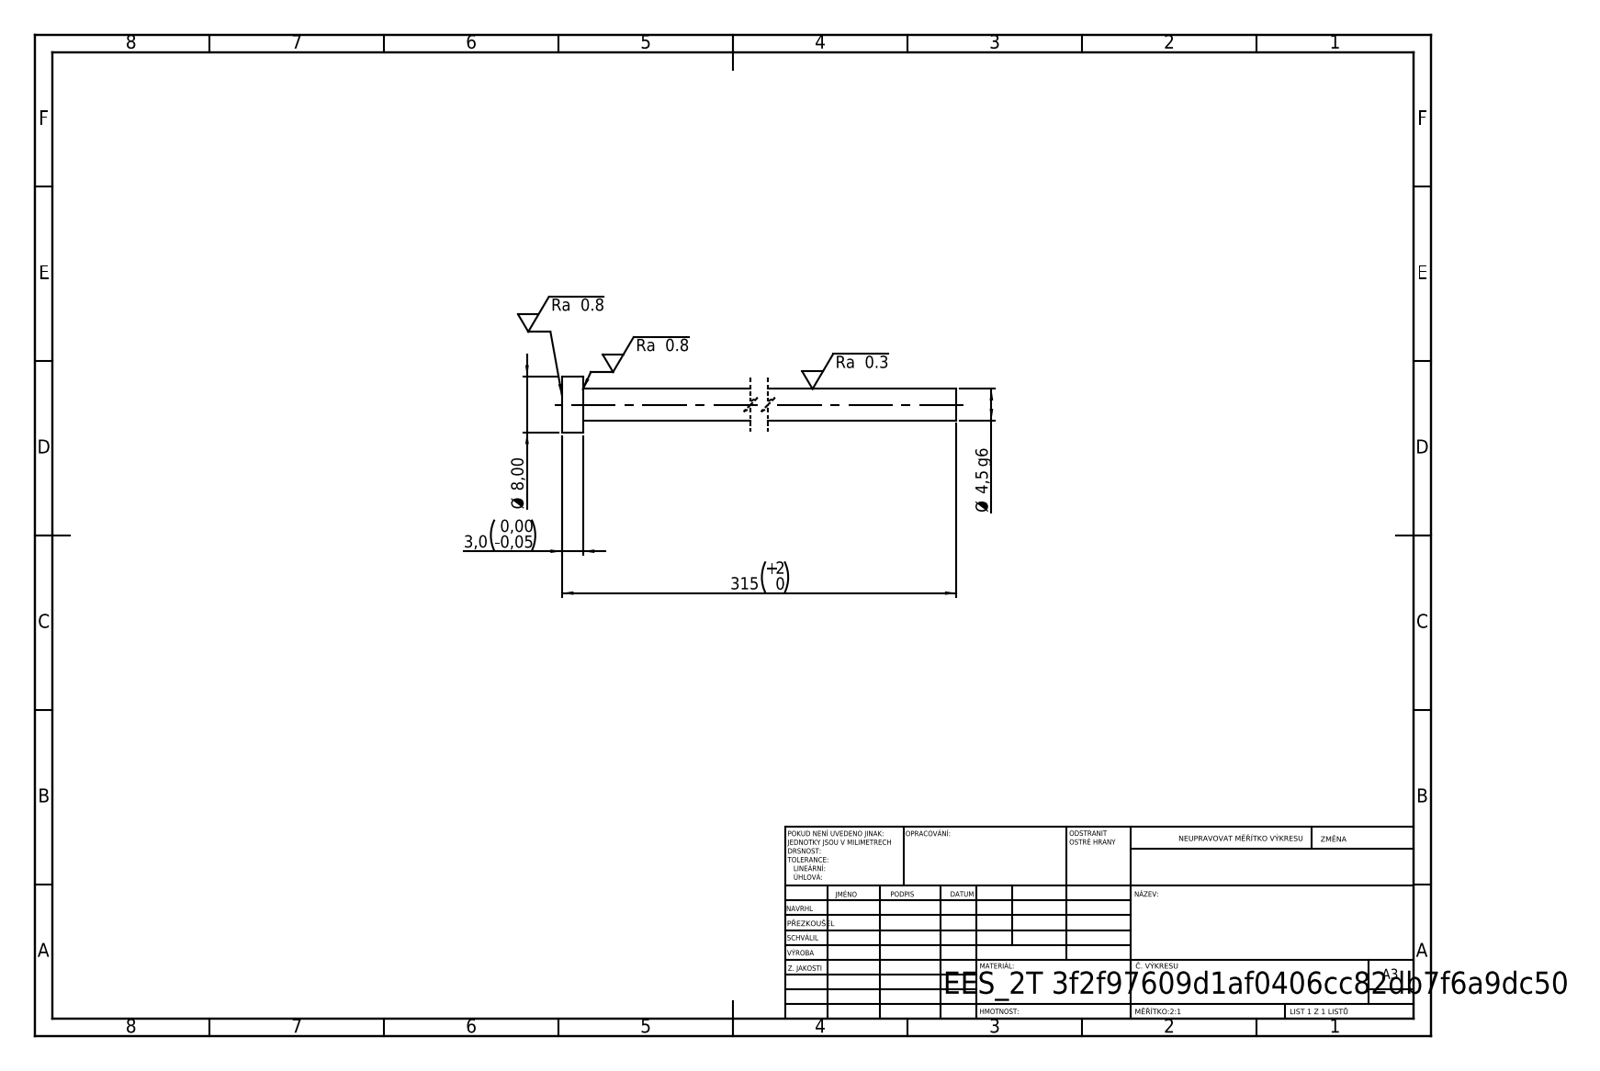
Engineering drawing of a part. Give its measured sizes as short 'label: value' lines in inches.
written by: SolidWorks 2019 (CONFIG_CONTROL_DESIGN)
unit: in
bodies: 1 solid, 7 faces (3 planar, 4 cylindrical, 0 other)
size: 12.402 × 0.315 × 0.315
volume: 0.312 in³; area: 7.11 in²
bosses: 1× ⌀0.315, 1× ⌀0.177
face distances: 0.118, 12.402, 12.283
